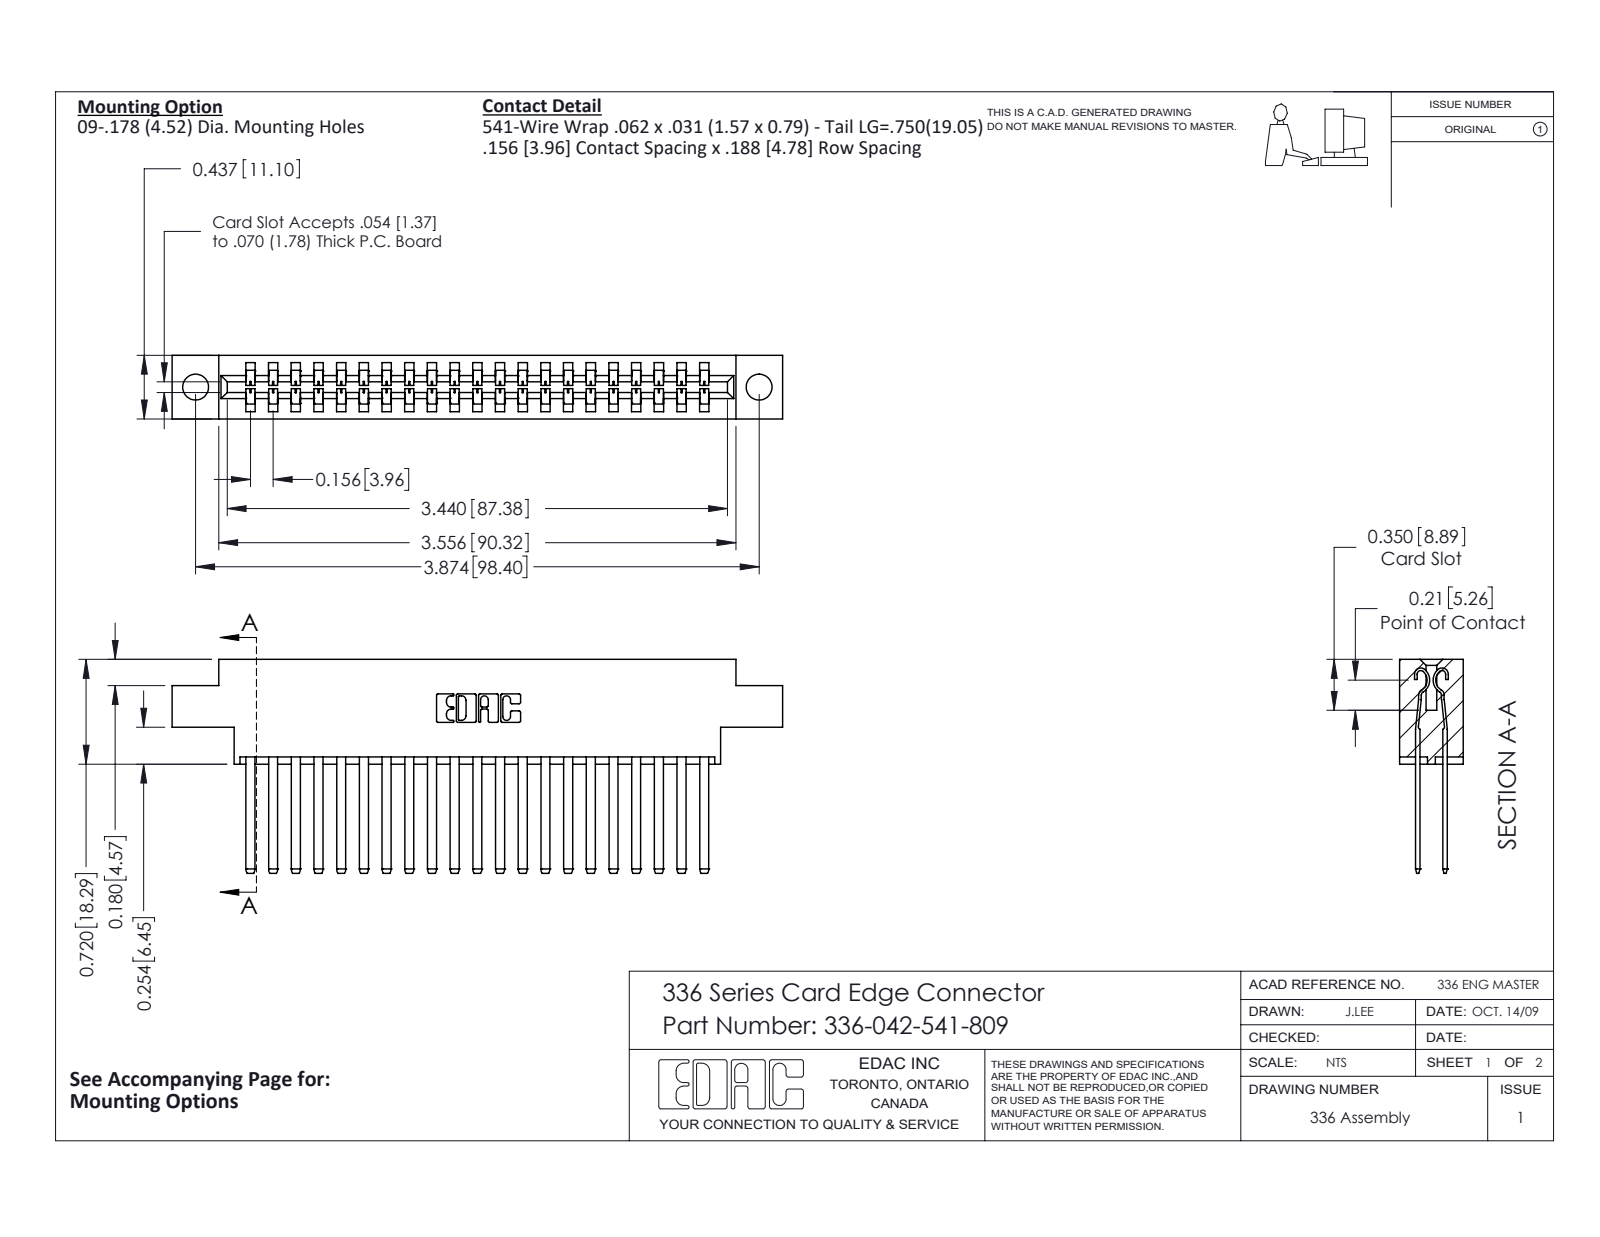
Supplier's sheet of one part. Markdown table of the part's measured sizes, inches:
| quantity | value |
| --- | --- |
| part name | 336-290-001_336-290-541; 336-042-541-809; 336 Part_Offset - .178 Dia - TH |
| STEP written by | SolidWorks 2020 (CONFIG_CONTROL_DESIGN) |
| units | inches |
| bodies | 43 solids, 1882 faces (1166 planar, 716 cylindrical, 0 other) |
| overall size | 4.197 × 1.47 × 0.437 |
| volume | 0.954 in³ |
| surface area | 30.28 in² |
| round holes (diameter × count) | 0.178 × 2 |
| partial cylindrical surfaces (radius × count) | 0.004 × 84, 0.056 × 42, 0.01 × 22, 0.007 × 6, 0.031 × 6, 0.022 × 4, 0.04 × 4, 0.026 × 3 |
| main face-to-face distances | 0.188, 0.328, 0.14, 0.297, 0.109, 0.031, 0.437, 0.033, 0.181, 0.256 |
| hole center spacings | 3.874 |
